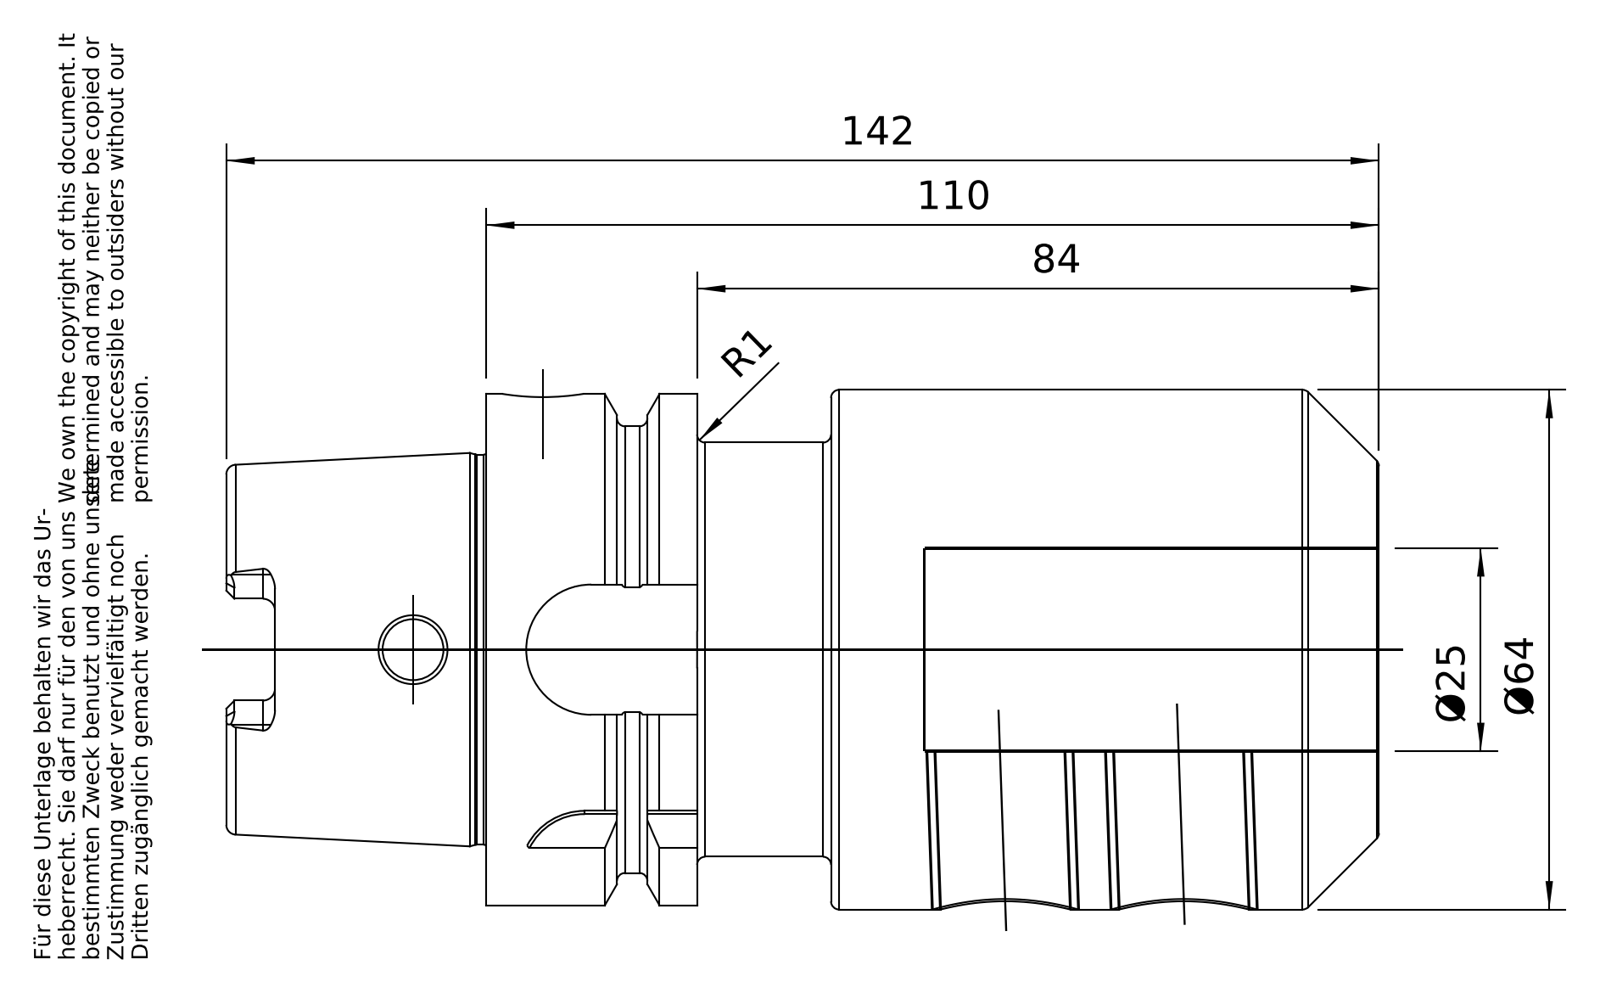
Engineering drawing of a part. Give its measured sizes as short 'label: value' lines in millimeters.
name: A63-030-25
written by: PRO/ENGINEER BY PARAMETRIC TECHNOLOGY CORPORATION, 2010430 (CONFIG_CONTROL_DESIGN)
unit: mm
bodies: 1 solid, 193 faces (60 planar, 59 cylindrical, 74 other)
size: 142 × 64 × 64
volume: 289 699 mm³; area: 47 699 mm²
holes: 2× ⌀16, 2× ⌀18, 1× ⌀7.5, 1× ⌀10, 1× ⌀16.92, 1× ⌀18.32, 1× ⌀18.66, 1× ⌀25, 1× ⌀34, 1× ⌀40
bosses: 1× ⌀64, 1× ⌀63, 1× ⌀55, 1× ⌀51, 1× ⌀48.04, 1× ⌀18
rounds: 6× R1.5, 4× R3, 1× R8, 1× R8.02, 1× R9.02
face distances: 110, 42.5, 67.5, 26, 16.5, 84, 10, 16, 32.5, 100
hole spacings: 22
